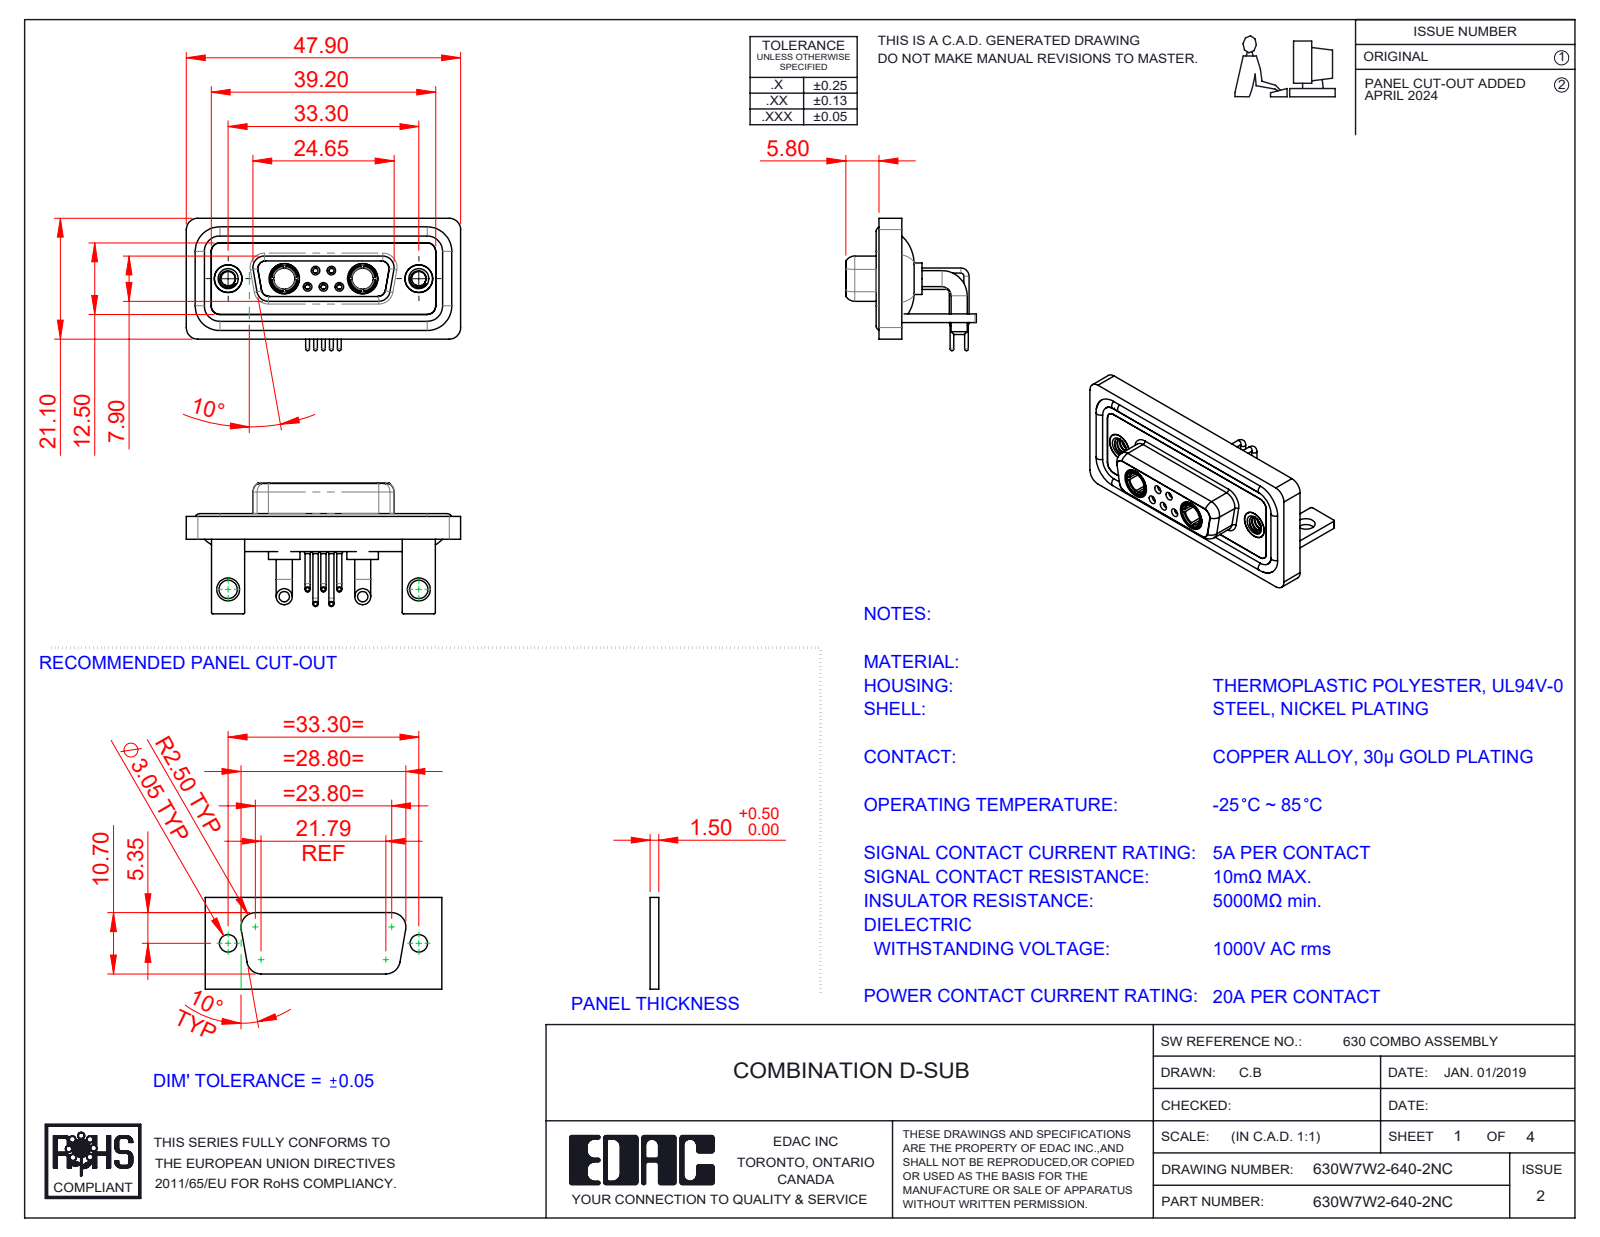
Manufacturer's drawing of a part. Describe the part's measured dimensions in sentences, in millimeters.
The part is named "630Combo Contact Row 2_50 Contacts; 630Combo Shell Rear_15 Contacts; 630Combo Housing_7W2; 630W7W2-640-2NC (+6 more)". Its 3-D file was written by "SolidWorks 2023 (CONFIG_CONTROL_DESIGN)". It is 18 solids with 849 faces: 258 planar, 375 cylindrical and 216 other. Overall it measures 47.9 by 23.12 by 22.8 millimeters. Its volume is 6 555 cubic millimeters and its surface area 10 944 square millimeters. Round holes: 5 of diameter 0.9, 5 of diameter 1.1, 5 of diameter 1.5, 5 of diameter 2, 4 of diameter 4.85, 3 of diameter 1.6, 2 of diameter 1.7, 2 of diameter 2.5, 2 of diameter 3.2, 2 of diameter 3.7, 2 of diameter 4, 2 of diameter 4.05. Round bosses or shafts: 6 of diameter 1.6, 5 of diameter 0.9, 5 of diameter 0.65, 4 of diameter 2.8, 2 of diameter 5.5, 2 of diameter 5.2, 2 of diameter 4.96, 2 of diameter 4.95. Partial cylindrical surfaces (rounded edges, fillets, slot ends): 21 of radius 2, 18 of radius 1.5, 16 of radius 0.25, 12 of radius 1.35, 8 of radius 1.6, 5 of radius 0.5, 4 of radius 0.6, 4 of radius 0.65. The main face-to-face distances are 0.4, 2.9, 1.5, 1.8, 3.7, 1.1, 4.1, 1.6, 2.5, 1.4. The hole center spacings are 3.16, 2.77, 9.8, 23.5, 33.3, 4.31, 4.33, 5.03.
